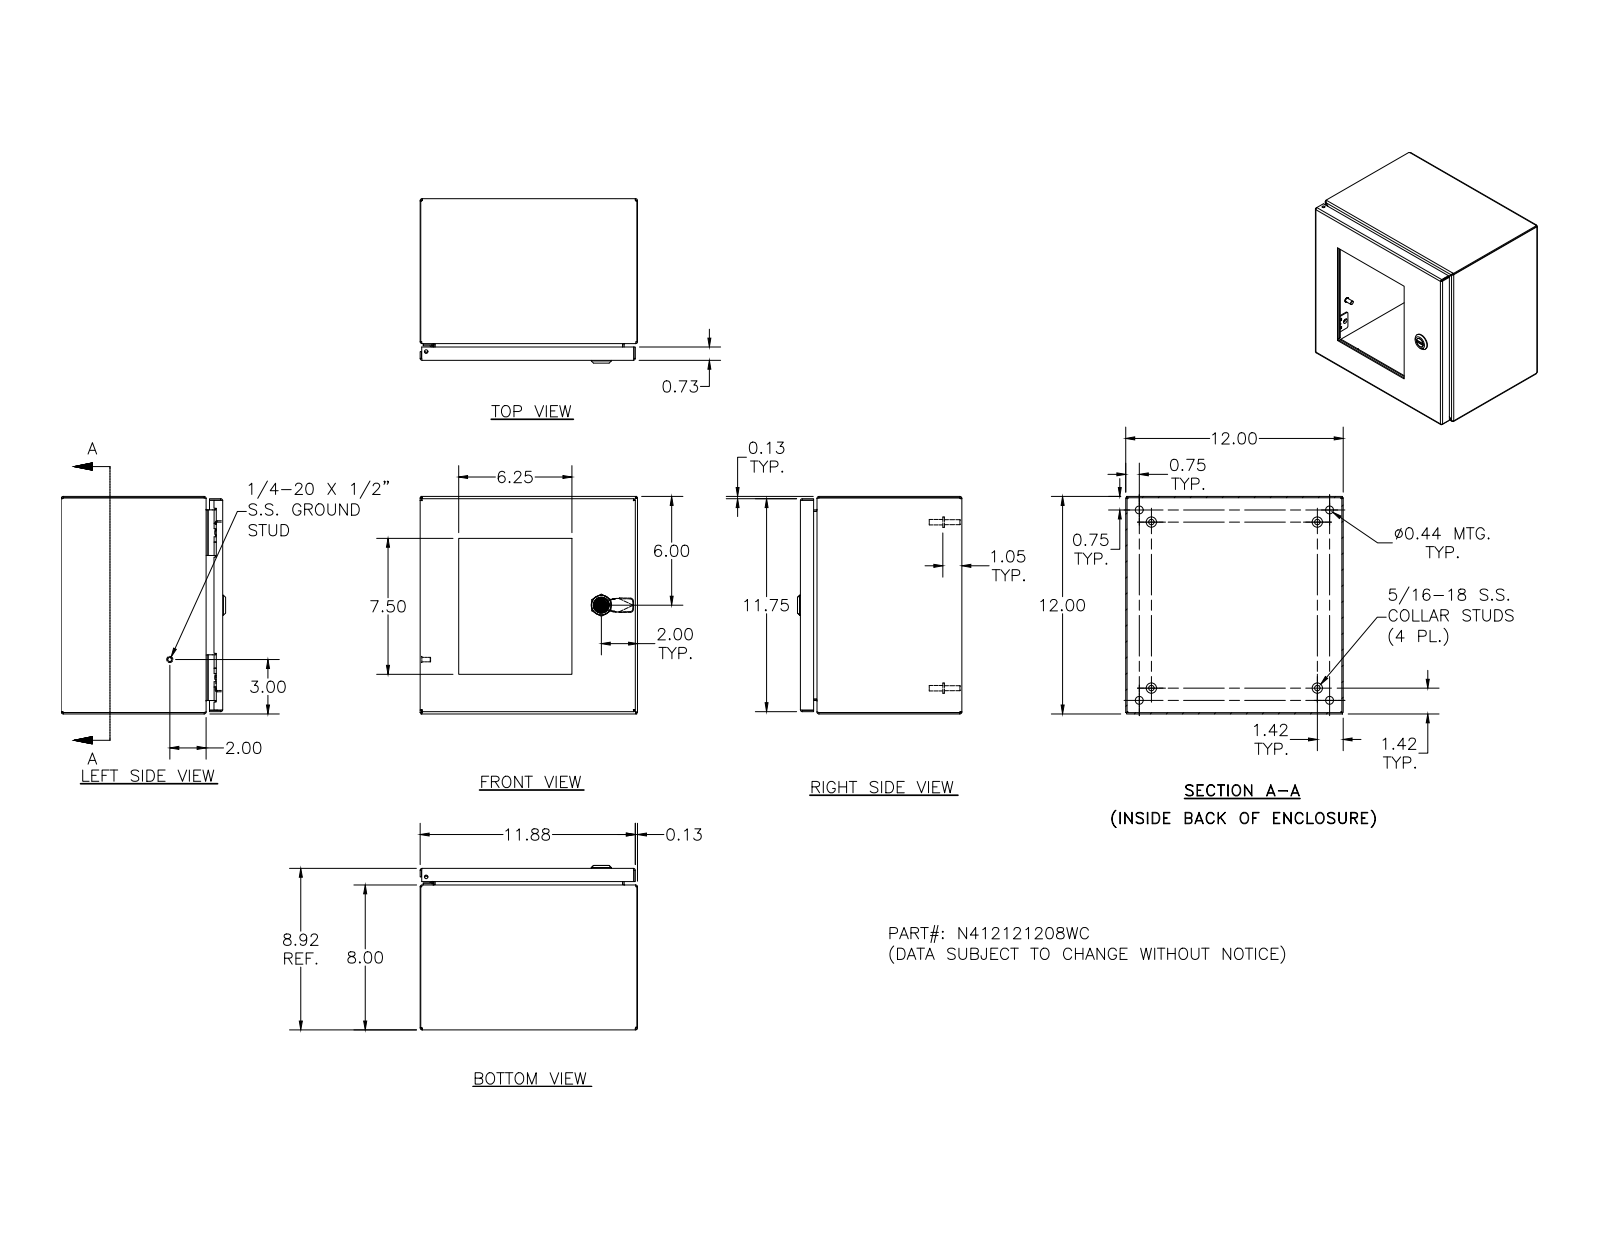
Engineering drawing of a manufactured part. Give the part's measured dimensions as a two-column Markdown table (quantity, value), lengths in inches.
| quantity | value |
| --- | --- |
| part name | N412121208WC |
| STEP written by | SolidWorks 2018 (AUTOMOTIVE_DESIGN) |
| units | inches |
| bodies | 53 solids, 1763 faces (665 planar, 585 cylindrical, 513 other) |
| overall size | 12 × 12 × 9.075 |
| volume | 72.22 in³ |
| surface area | 1 690 in² |
| round holes (diameter × count) | 0.156 × 10, 0.281 × 8, 0.188 × 5, 0.093 × 4, 0.152 × 4, 0.167 × 4, 0.172 × 4, 0.437 × 4, 0.187 × 1, 0.197 × 1, 0.315 × 1, 0.394 × 1 |
| round bosses / shafts (diameter × count) | 0.25 × 10, 0.337 × 8, 0.19 × 8, 0.563 × 4, 0.36 × 4, 0.32 × 4, 0.3 × 4, 0.275 × 4 |
| partial cylindrical surfaces (radius × count) | 0.031 × 34, 0.012 × 30, 0.05 × 26, 0.105 × 24, 0.016 × 18, 0.125 × 16, 0.02 × 13, 0.032 × 8 |
| main face-to-face distances | 0.074, 11.926, 8.843, 12, 11.852, 8.769, 8.917, 0.25, 8.593, 8.519 |
| hole center spacings | 8, 4, 6.221, 8.585, 10.5, 8.927, 0.5, 0.656 |
